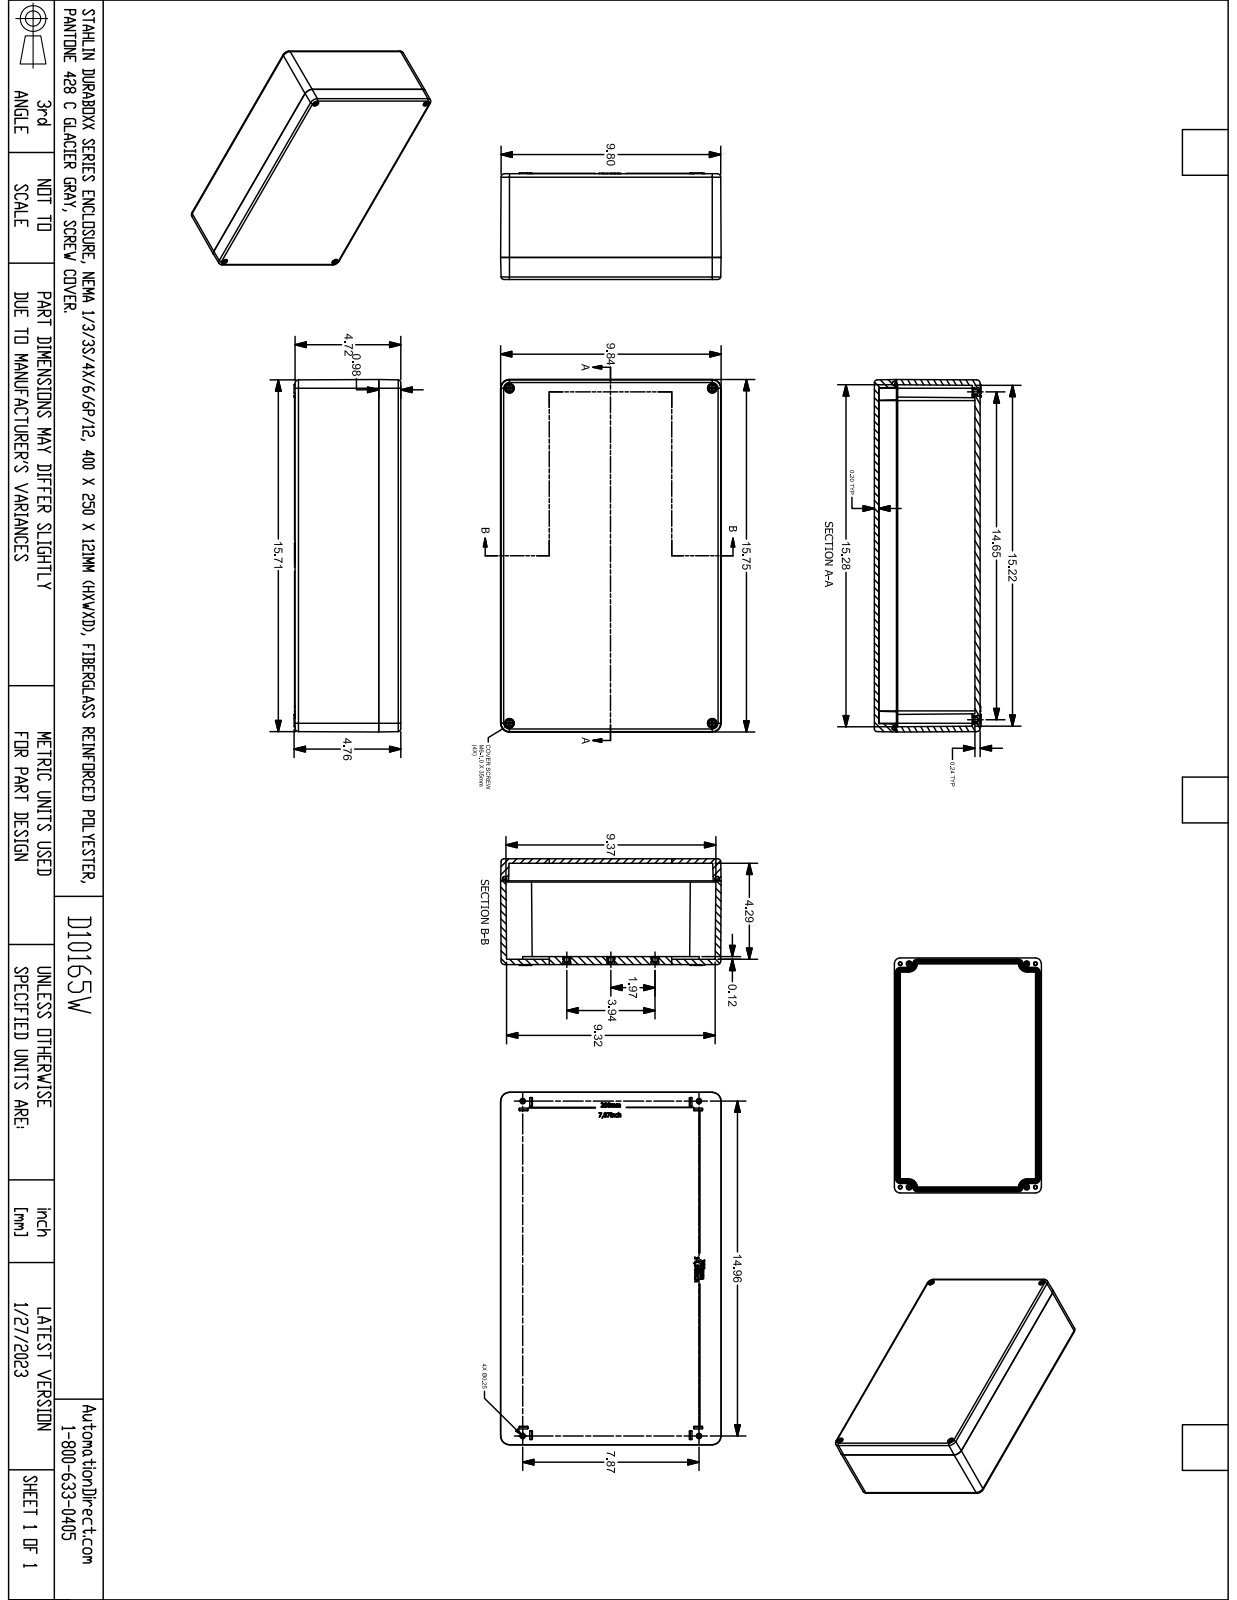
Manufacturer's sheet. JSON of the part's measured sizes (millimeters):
{"part_name": "DU10165W", "step_written_by": "SolidWorks 2018 (AUTOMOTIVE_DESIGN)", "units": "millimeters", "bodies": {"solids": 17, "faces": 1274, "planar": 623, "cylindrical": 170, "other": 481}, "overall_size": [400, 250, 121], "volume_mm3": 2137000, "surface_area_mm2": 756100, "round_holes": [[4.9, 10], [6, 6], [5.4, 4], [7, 4]], "round_bosses_or_shafts": [[7.4, 10], [9.5, 4], [8, 4], [6, 4], [5.2, 4]], "partial_cylinders_radius": [[0.5, 32], [2.3, 12], [4.2, 8], [8.7, 8], [0.4, 6], [3, 4], [3.3, 4], [3.3, 4]], "face_to_face_distances": [120, 115, 5, 114, 6, 109, 25, 20, 89, 95], "hole_center_spacings": [50, 65.1, 115.1, 165, 375.4, 381.6, 393.2, 410.6]}
